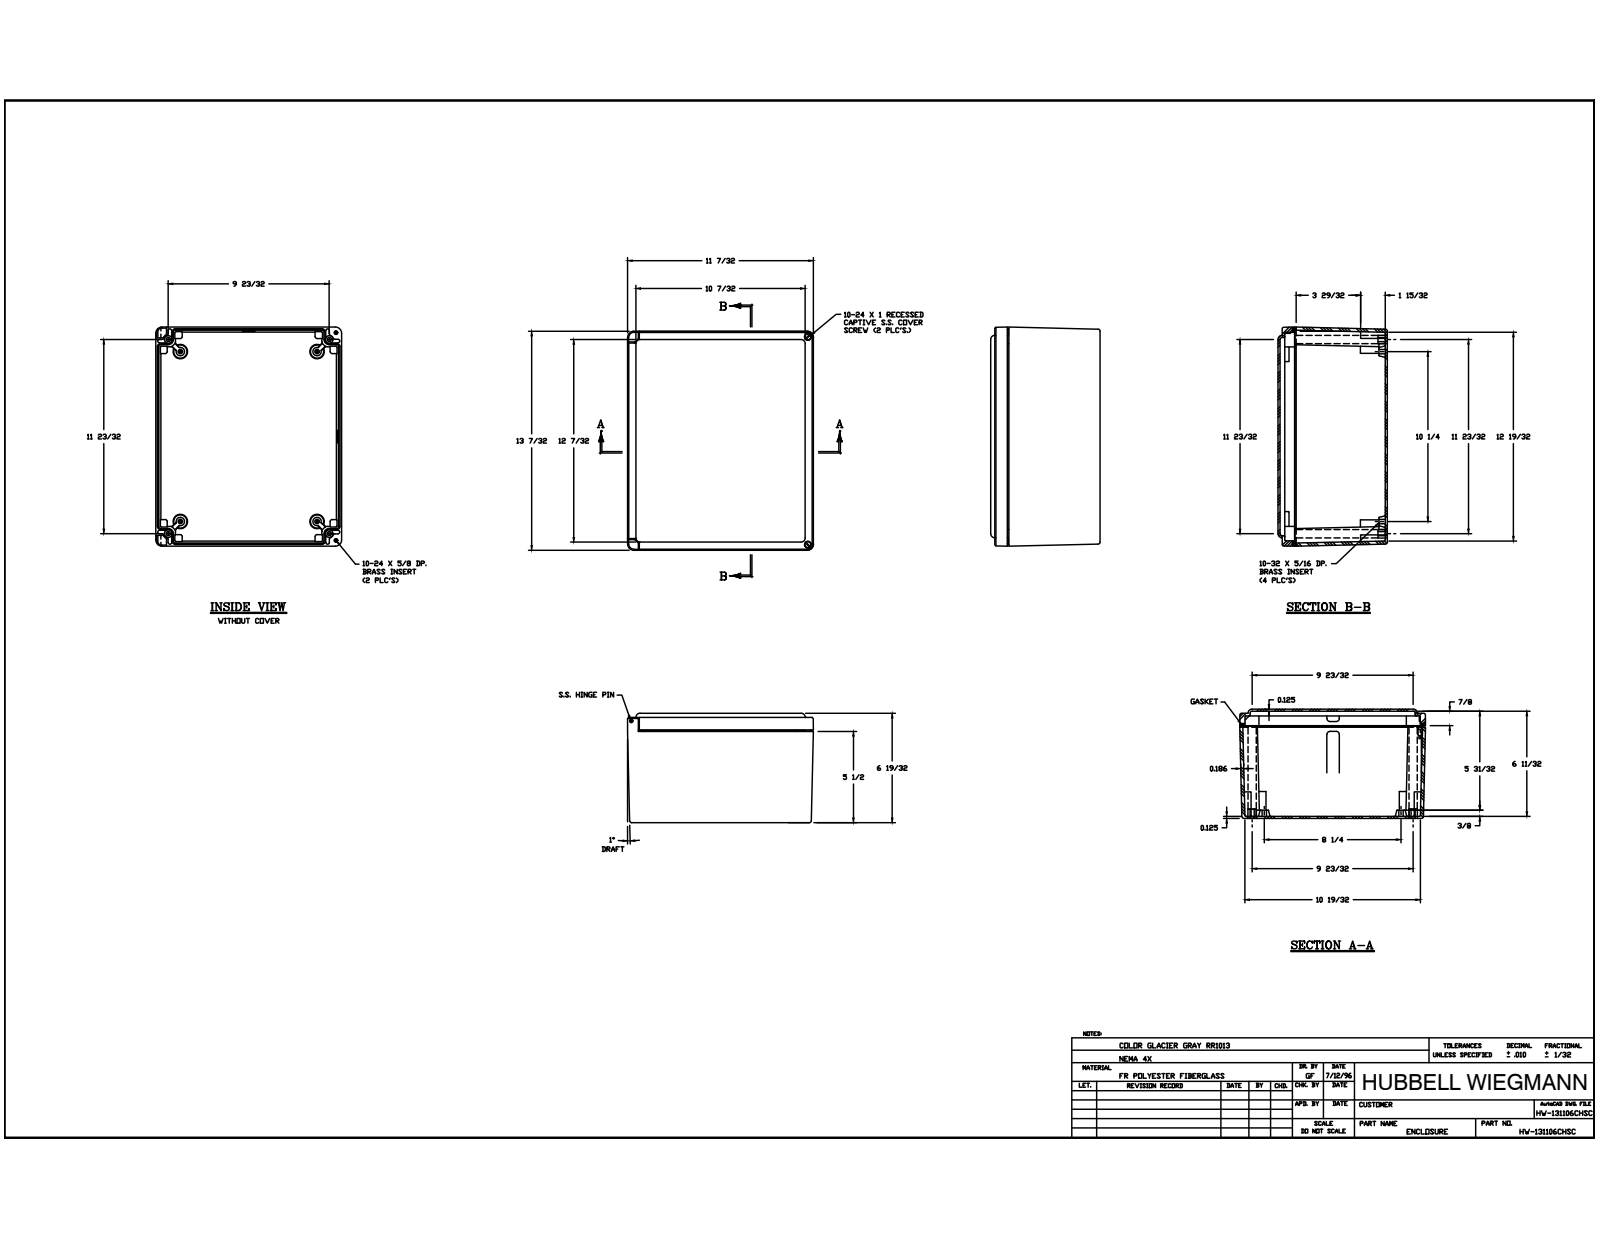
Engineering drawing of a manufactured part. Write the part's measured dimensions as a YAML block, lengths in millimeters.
part_name: "WP1311HWBOX; 0.3125-18 X 0.563 DP BRASS INSERT; 10-32 X0.3125 DP BRASS INSERT; 10-24 X 0.625 DP BRASS INSERT (+8 more)"
step_written_by: "Autodesk Inventor 2014 (AUTOMOTIVE_DESIGN)"
units: millimeters
bodies: {solids: 23, faces: 1024, planar: 398, cylindrical: 294, other: 332}
overall_size: [335.76, 284.96, 167.48]
volume: 1791000
surface_area: 836082
round_holes:
  - {diameter: 7.14, count: 6}
  - {diameter: 3.96, count: 4}
  - {diameter: 7.94, count: 4}
  - {diameter: 13.49, count: 4}
  - {diameter: 2.44, count: 2}
  - {diameter: 3.68, count: 2}
  - {diameter: 3.97, count: 2}
  - {diameter: 4.83, count: 2}
  - {diameter: 5.56, count: 2}
  - {diameter: 5.84, count: 2}
  - {diameter: 7.1, count: 2}
  - {diameter: 10.32, count: 2}
round_bosses_or_shafts:
  - {diameter: 9.52, count: 2}
  - {diameter: 9.24, count: 2}
  - {diameter: 5.94, count: 2}
  - {diameter: 4.86, count: 2}
  - {diameter: 2.42, count: 2}
  - {diameter: 9.42, count: 1}
  - {diameter: 4.52, count: 1}
  - {diameter: 2.24, count: 1}
partial_cylinders:
  - {radius: 0.79, count: 60}
  - {radius: 3.17, count: 38}
  - {radius: 1.59, count: 30}
  - {radius: 0.25, count: 8}
  - {radius: 1.5, count: 8}
  - {radius: 4.78, count: 8}
  - {radius: 6.35, count: 8}
  - {radius: 9.53, count: 8}
face_to_face_distances: [3.17, 164.31, 4.72, 167.48, 161.14, 3.18, 6.35, 161.13, 157.96, 19.05]
hole_center_spacings: [26.38, 40.98, 228.95, 240.27, 257.38, 270.68, 279.61, 290.76]
